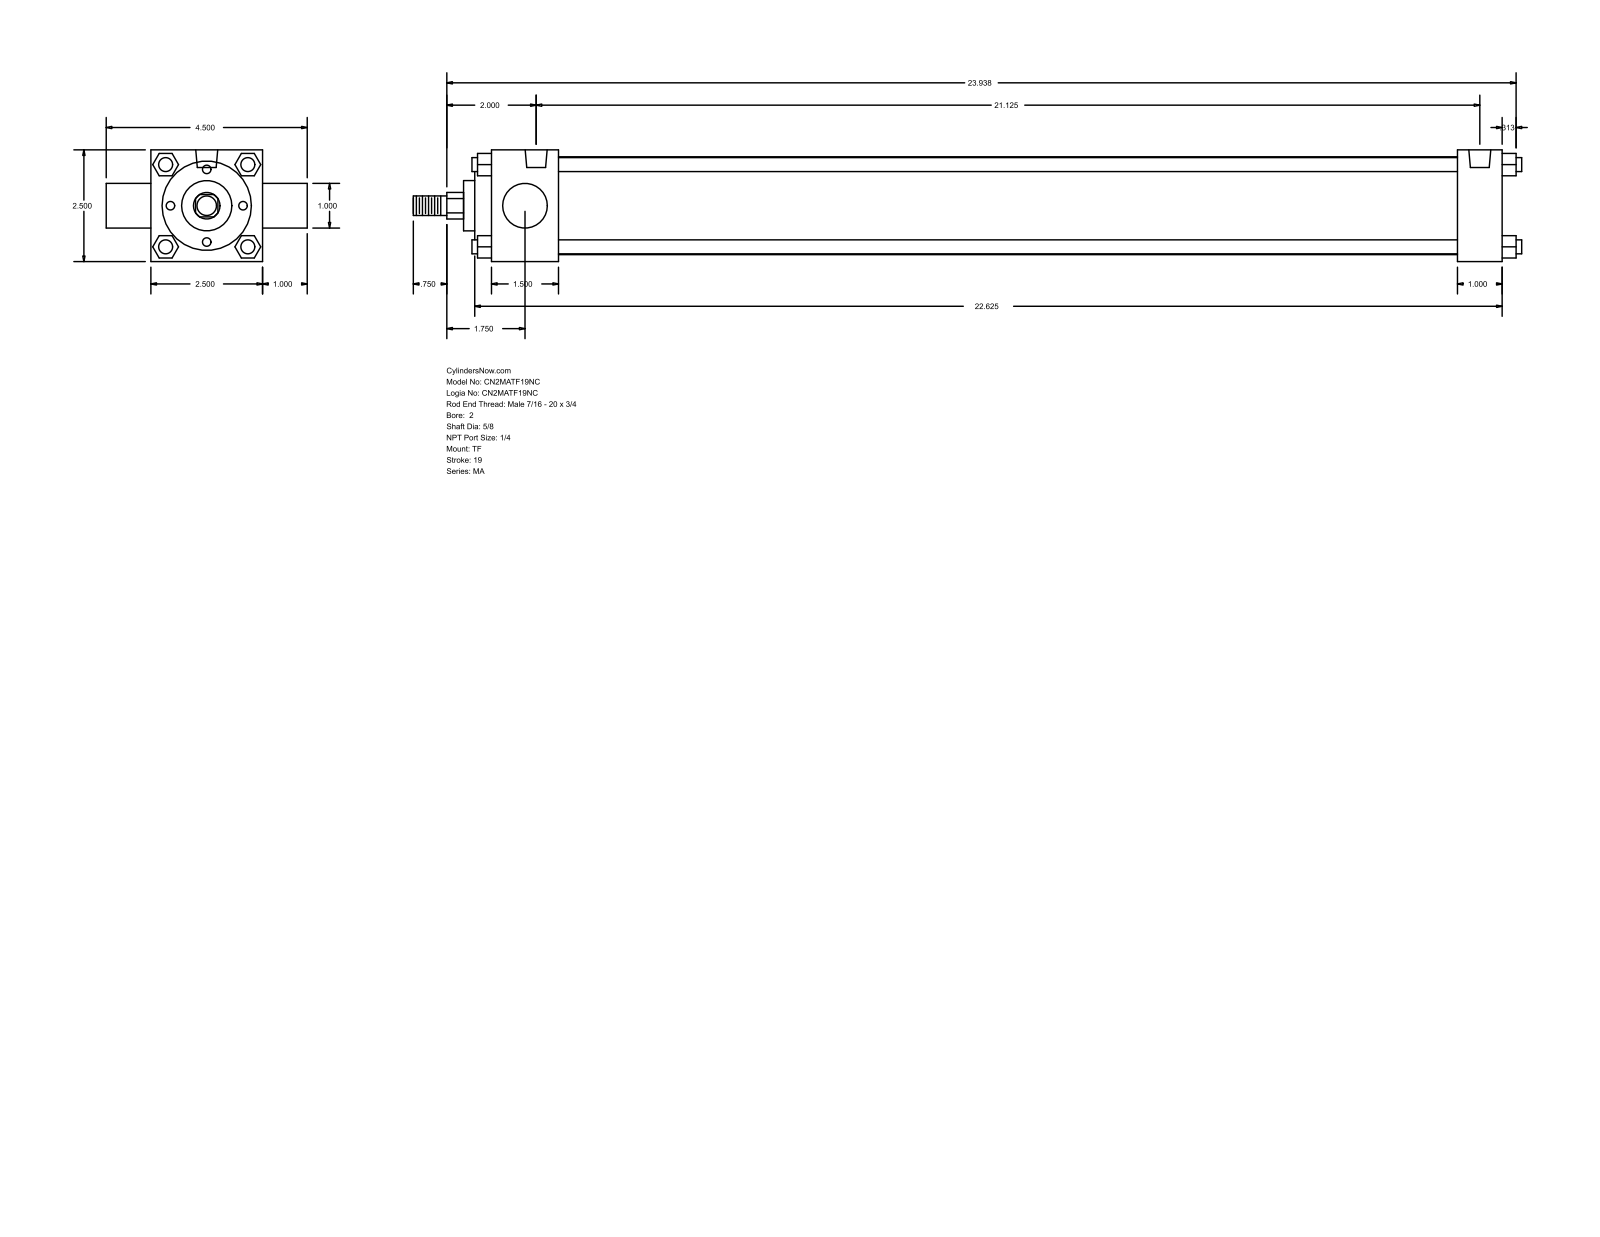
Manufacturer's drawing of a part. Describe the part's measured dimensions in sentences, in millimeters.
The part is named "MA_TF__0200_0.625". Its 3-D file was written by "GSSL Pune (CONFIG_CONTROL_DESIGN)". It is 0 solids with 122 faces: 93 planar, 29 cylindrical and 0 other. Overall it measures 630.24 by 114.3 by 63.5 millimeters. Round holes: 3 of diameter 7.94, 2 of diameter 12.49. Round bosses or shafts: 4 of diameter 7.94, 1 of diameter 55.63, 1 of diameter 50.8, 1 of diameter 28.57, 1 of diameter 25.4, 1 of diameter 15.88, 1 of diameter 11.11. Partial cylindrical surfaces (rounded edges, fillets, slot ends): 1 of radius 7.54. The main face-to-face distances are 63.5, 38.1, 12.7, 574.68, 549.27, 511.17, 536.58, 25.41, 9.52, 47.62. The hole center spacings are 536.58.
